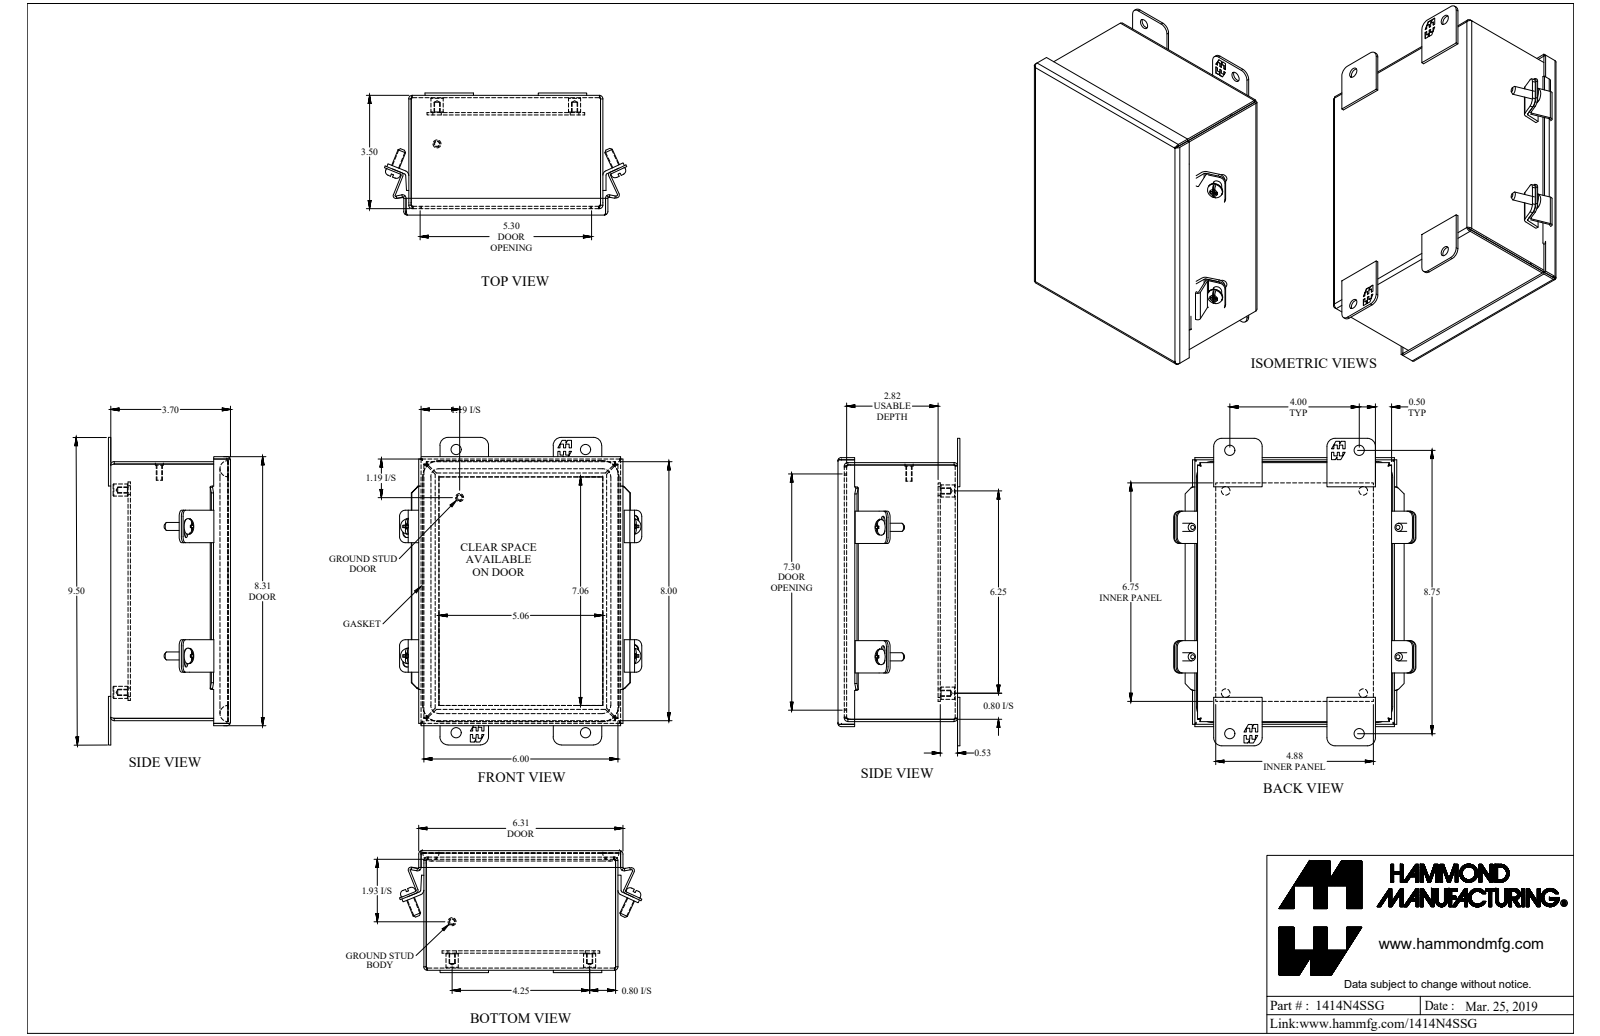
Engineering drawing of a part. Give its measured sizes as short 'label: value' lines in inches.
name: 1414N4SSG
written by: SolidWorks 2018 (AUTOMOTIVE_DESIGN)
unit: in
bodies: 26 solids, 717 faces (473 planar, 168 cylindrical, 76 other)
size: 9.5 × 7.488 × 3.769
volume: 22.2 in³; area: 615.8 in²
holes: 4× ⌀0.156, 4× ⌀0.213, 4× ⌀0.265, 4× ⌀0.313
bosses: 6× ⌀0.25, 4× ⌀0.48, 4× ⌀0.375, 2× ⌀0.19
rounds: 24× R0.25, 16× R0.188, 10× R0.036, 10× R0.108, 8× R0.141, 4× R0.007, 4× R0.01, 4× R0.029
face distances: 0.072, 3.625, 3.093, 0.532, 3.697, 5.928, 3.553, 0.604, 7.928, 3.165
hole spacings: 1.256, 4, 4.31, 7.501, 8.559, 4.25, 6.25, 7.558
